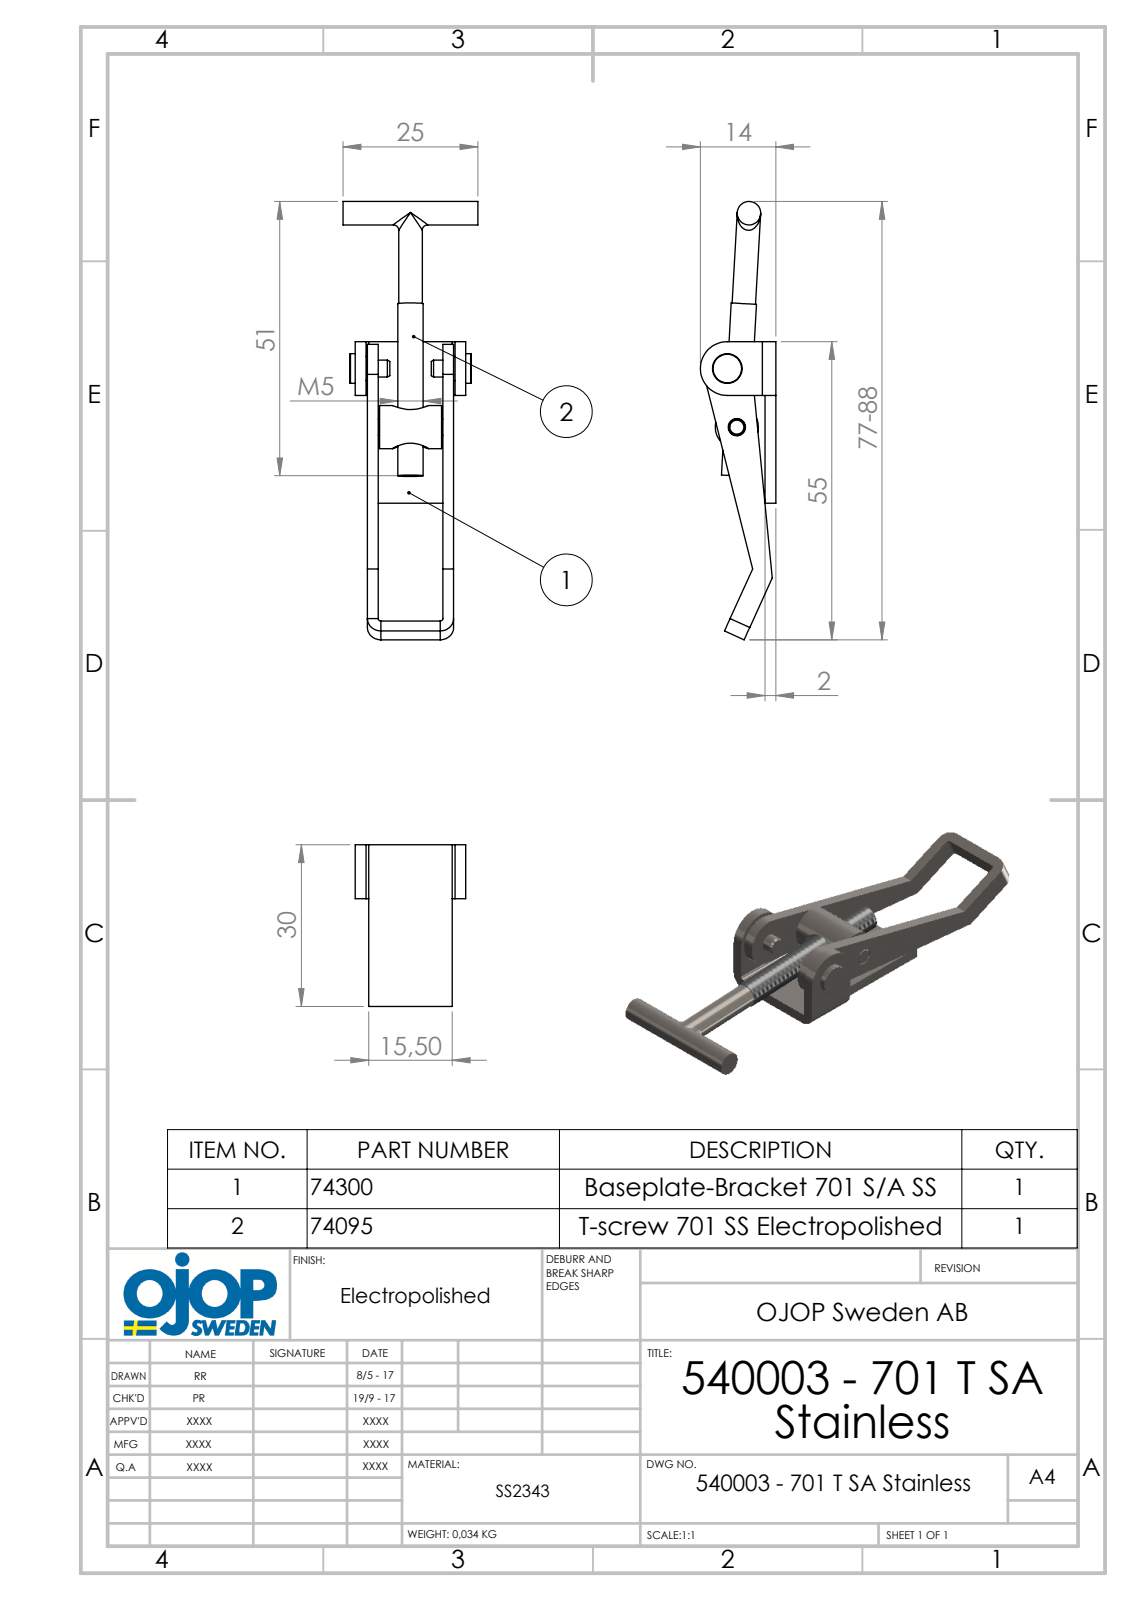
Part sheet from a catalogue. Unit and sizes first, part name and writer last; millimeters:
Units: millimetres
Overall size (bounding box): 80.46 × 25 × 14
Round holes (diameter × count): ⌀3.2 ×2, ⌀4.5 ×1, ⌀4.8 ×1
Round bosses / shafts (diameter × count): ⌀4.36 ×2, ⌀8 ×1, ⌀5.5 ×1, ⌀4.7 ×1, ⌀3.15 ×1, ⌀3 ×1
Partial cylindrical surfaces — rounded edges, fillets, slot ends (radius × count): R0.5 ×4, R2.5 ×4, R4.5 ×1, R5 ×1
Main face-to-face distances: 2, 14, 2.25, 16, 16.25, 12, 4.25, 18.25, 18.5, 14.25
Hole centre spacings: 11.03
Volume: 4 448 mm³ · Surface area: 5 385 mm²
Bodies: 6 solids, 121 faces (51 planar, 52 cylindrical, 18 other)
Part name (STEP PRODUCT): 701 - Mid Cylinder; 720951 - T-skruv 701 FZB; 540003; 701 - SA (+2 more)
STEP written by: SolidWorks 2015 (AUTOMOTIVE_DESIGN)
